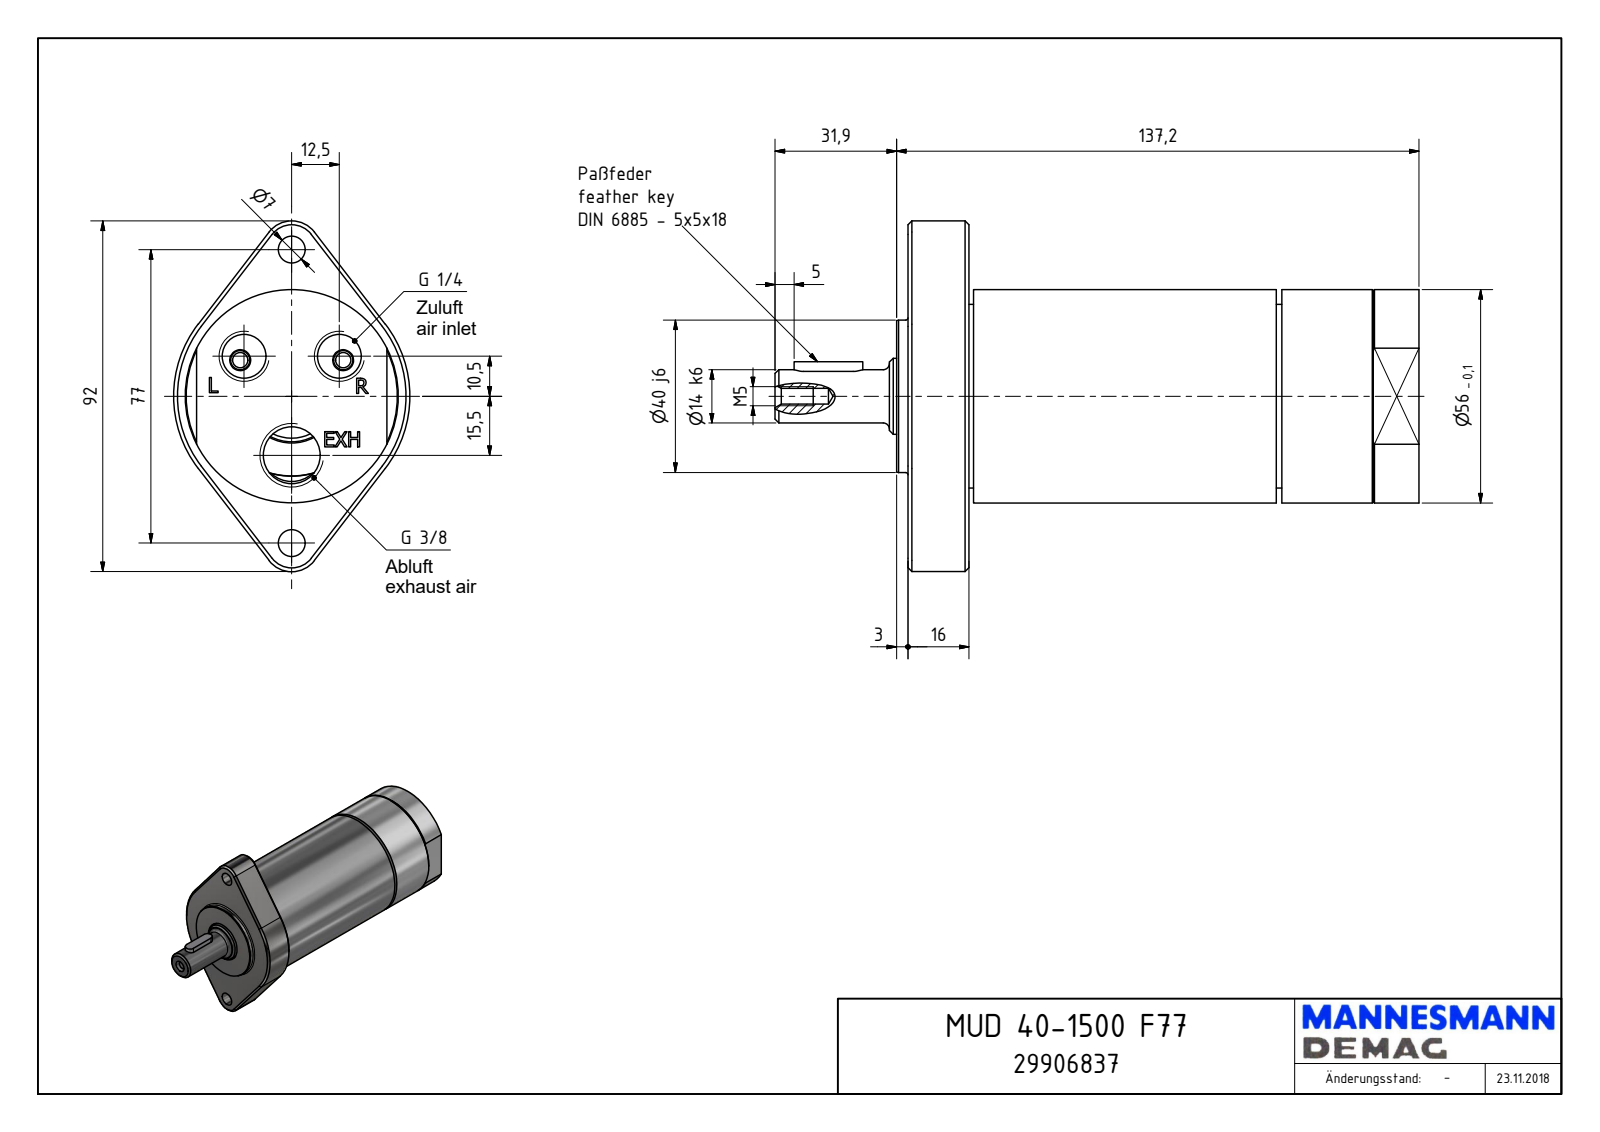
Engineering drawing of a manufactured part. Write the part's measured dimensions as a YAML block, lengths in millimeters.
part_name: "MUD 40-1500_29906835"
step_written_by: "Autodesk Inventor 2008 (CONFIG_CONTROL_DESIGN)"
units: millimeters
bodies: {solids: 1, faces: 72, planar: 29, cylindrical: 16, other: 27}
overall_size: [169.1, 92, 62]
volume: 352018
surface_area: 37774
round_bosses_or_shafts:
  - {diameter: 56, count: 1}
  - {diameter: 52.62, count: 1}
  - {diameter: 40, count: 1}
  - {diameter: 19.95, count: 1}
  - {diameter: 14, count: 1}
partial_cylinders:
  - {radius: 2.5, count: 2}
  - {radius: 7.5, count: 2}
  - {radius: 11, count: 1}
  - {radius: 23, count: 1}
  - {radius: 31, count: 1}
face_to_face_distances: [134.2, 16, 118.2, 3, 19, 137.2, 124.24, 121.24, 105.24, 12.96]
